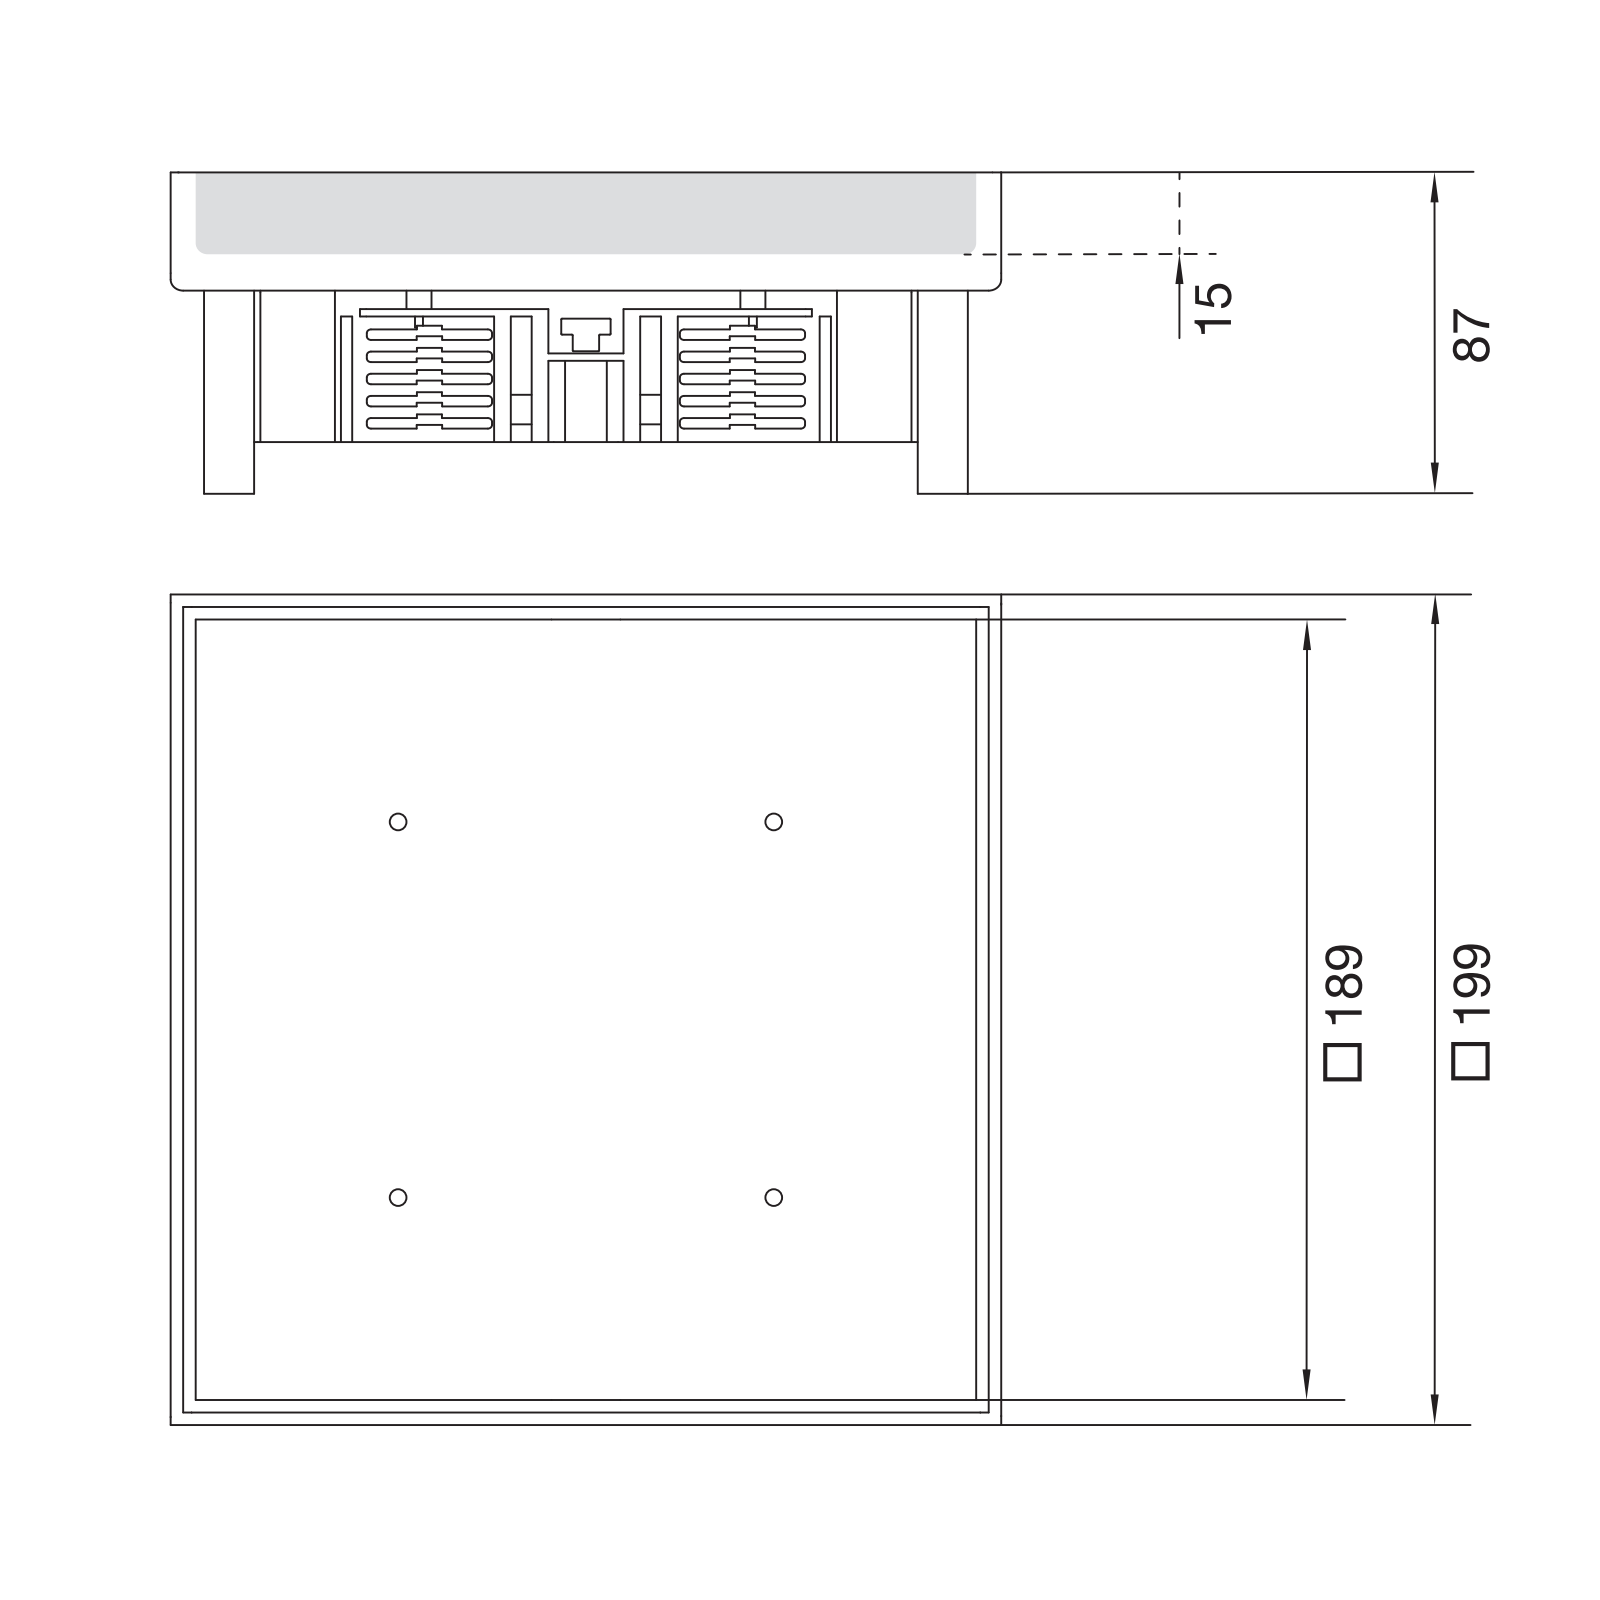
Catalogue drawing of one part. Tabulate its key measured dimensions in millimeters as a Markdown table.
| quantity | value |
| --- | --- |
| part name | T-00597; T-00595; T-00806_ASM; U09001 (+4 more) |
| STEP written by | CREO PARAMETRIC BY PTC INC, 2022024 (AUTOMOTIVE_DESIGN) |
| units | millimeters |
| bodies | 8 solids, 201 faces (127 planar, 74 cylindrical, 0 other) |
| overall size | 199 × 199 × 87 |
| volume | 505 215 mm³ |
| surface area | 308 113 mm² |
| round holes (diameter × count) | 5 × 4, 6.8 × 4, 8.5 × 4, 117 × 1 |
| round bosses / shafts (diameter × count) | 12 × 4, 9.85 × 4 |
| partial cylindrical surfaces (radius × count) | 1 × 8, 3 × 8, 105 × 5, 2 × 4, 107 × 1 |
| main face-to-face distances | 2, 3, 10, 15, 12, 5, 197, 2.5, 194, 17 |
| hole center spacings | 136.64, 57.28, 63.64, 90, 120.92, 171, 184.55, 127.28 |
